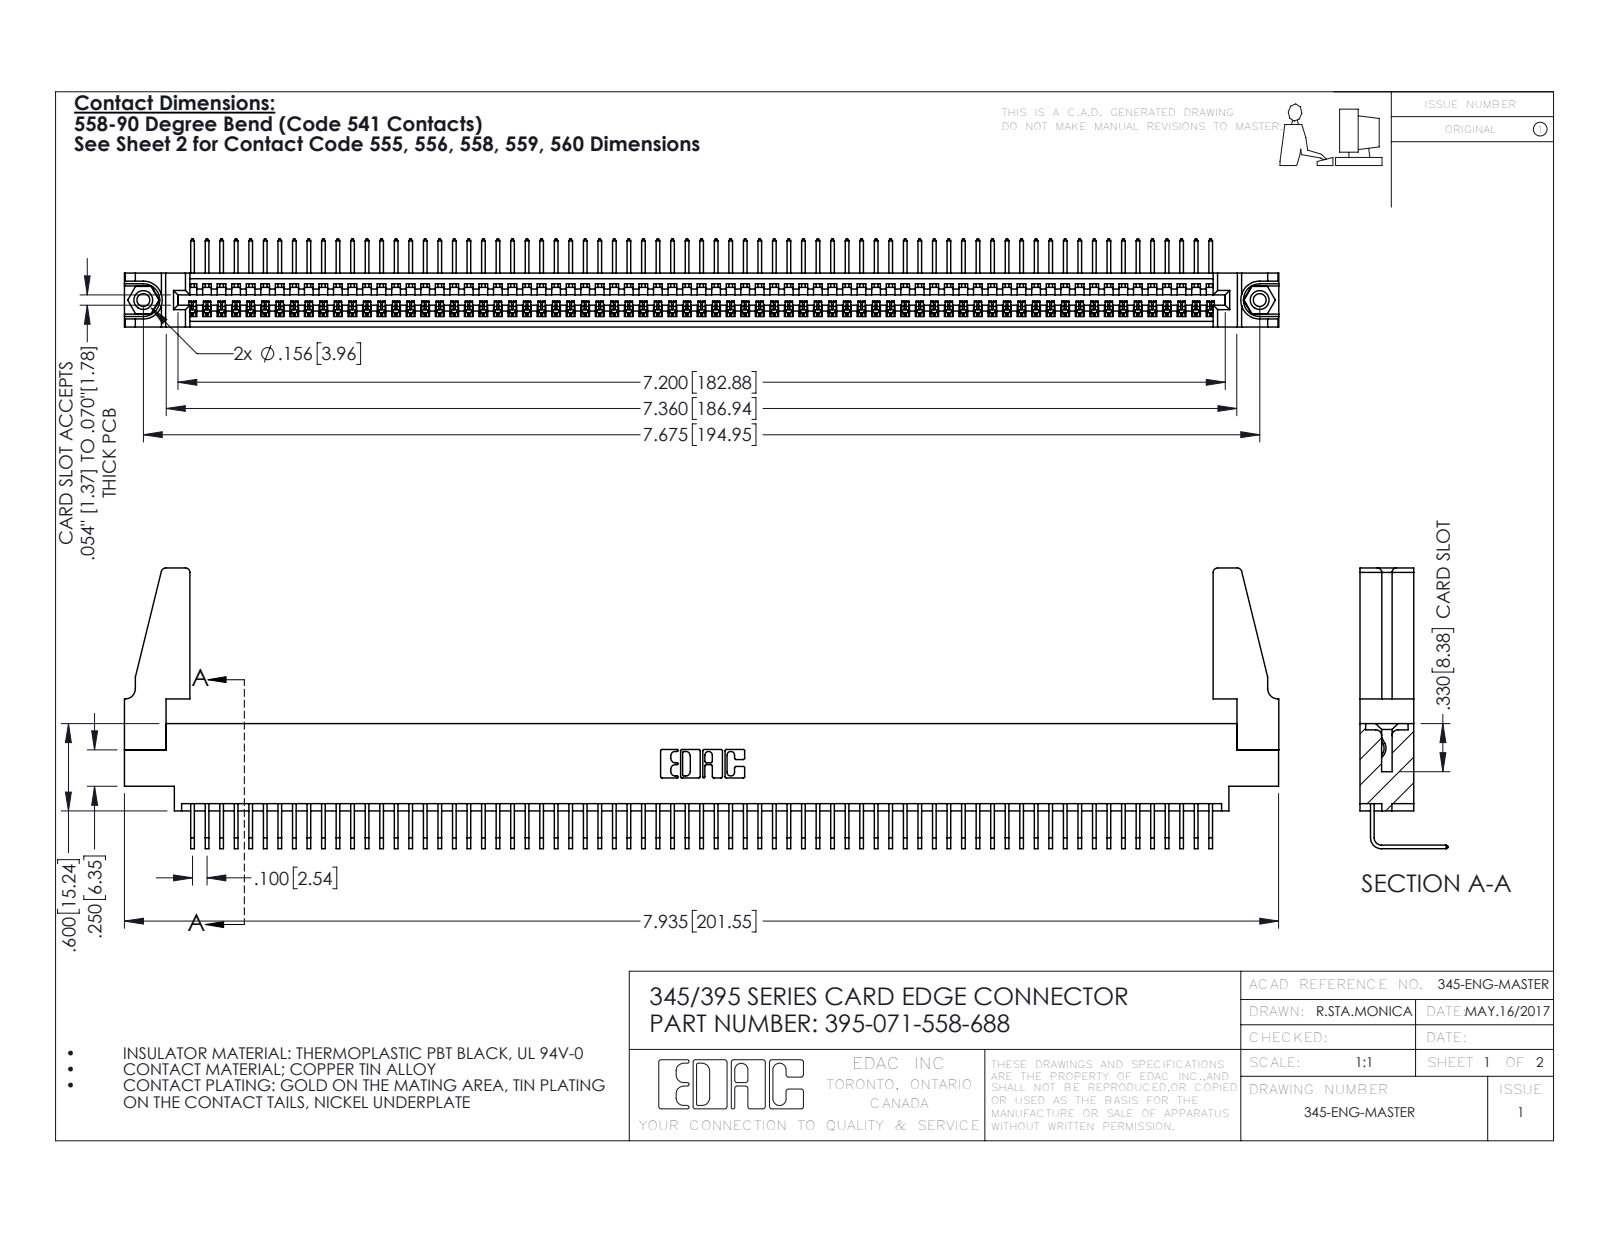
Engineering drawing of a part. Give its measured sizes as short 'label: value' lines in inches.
name: 345 Part_0.170 Offset - 0.156 Dia-TH; 345-250-001_345-250-001-102; 345-220-078_345-220-088; 345-292-001_558 Tail - 2 (+1 more)
written by: SolidWorks 2016 (CONFIG_CONTROL_DESIGN)
unit: in
bodies: 76 solids, 4514 faces (3138 planar, 1360 cylindrical, 16 other)
size: 7.936 × 1.929 × 0.605
volume: 1.389 in³; area: 47.99 in²
holes: 2× ⌀0.089, 2× ⌀0.125, 2× ⌀0.156, 1× ⌀0.064
bosses: 2× ⌀0.155
rounds: 142× R0.006, 22× R0.01, 8× R0.03, 6× R0.007, 6× R0.031, 3× R0.026, 2× R0.031, 2× R0.04
face distances: 0.072, 0.298, 0.37, 0.098, 0.272, 0.025, 0.2, 0.225, 0.175, 0.149
hole spacings: 0.27, 7.439, 7.675
